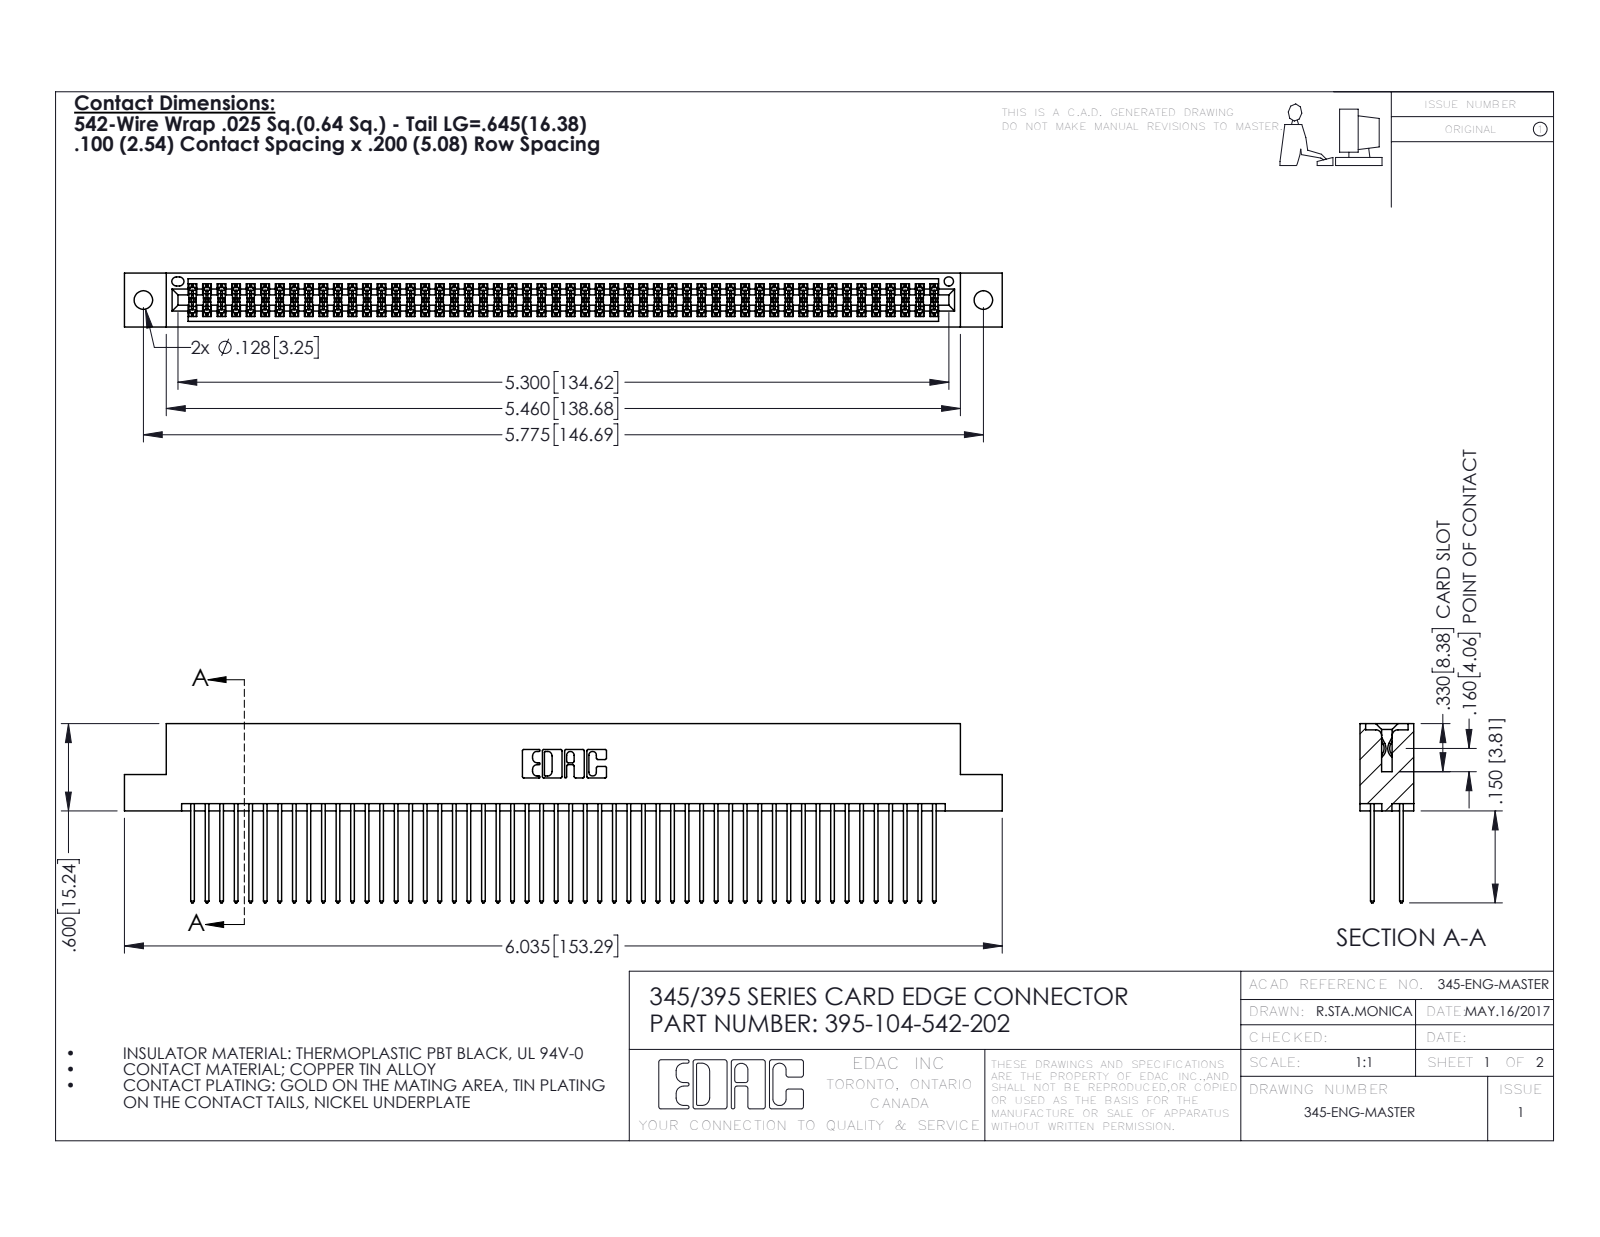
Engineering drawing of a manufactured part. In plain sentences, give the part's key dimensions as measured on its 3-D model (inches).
The part is named "395-104-542-202; 345 Part_Flush Mounting Lugs - 0.128 Dia; 345-292-001_345-293-142". Its 3-D file was written by "SolidWorks 2016 (CONFIG_CONTROL_DESIGN)". It is 105 solids with 5326 faces: 3512 planar, 1814 cylindrical and 0 other. Overall it measures 6.035 by 1.232 by 0.37 inches. Its volume is 0.942 cubic inches and its surface area 38.75 square inches. Round holes: 2 of diameter 0.128, 1 of diameter 0.064. Partial cylindrical surfaces (rounded edges, fillets, slot ends): 156 of radius 0.006, 104 of radius 0.01, 22 of radius 0.01, 6 of radius 0.007, 6 of radius 0.031, 3 of radius 0.026, 2 of radius 0.014, 2 of radius 0.019. The main face-to-face distances are 0.298, 0.072, 0.2, 0.098, 0.272, 0.025, 0.225, 0.37, 0.175, 0.149. The hole center spacings are 0.27, 5.539, 5.775.
